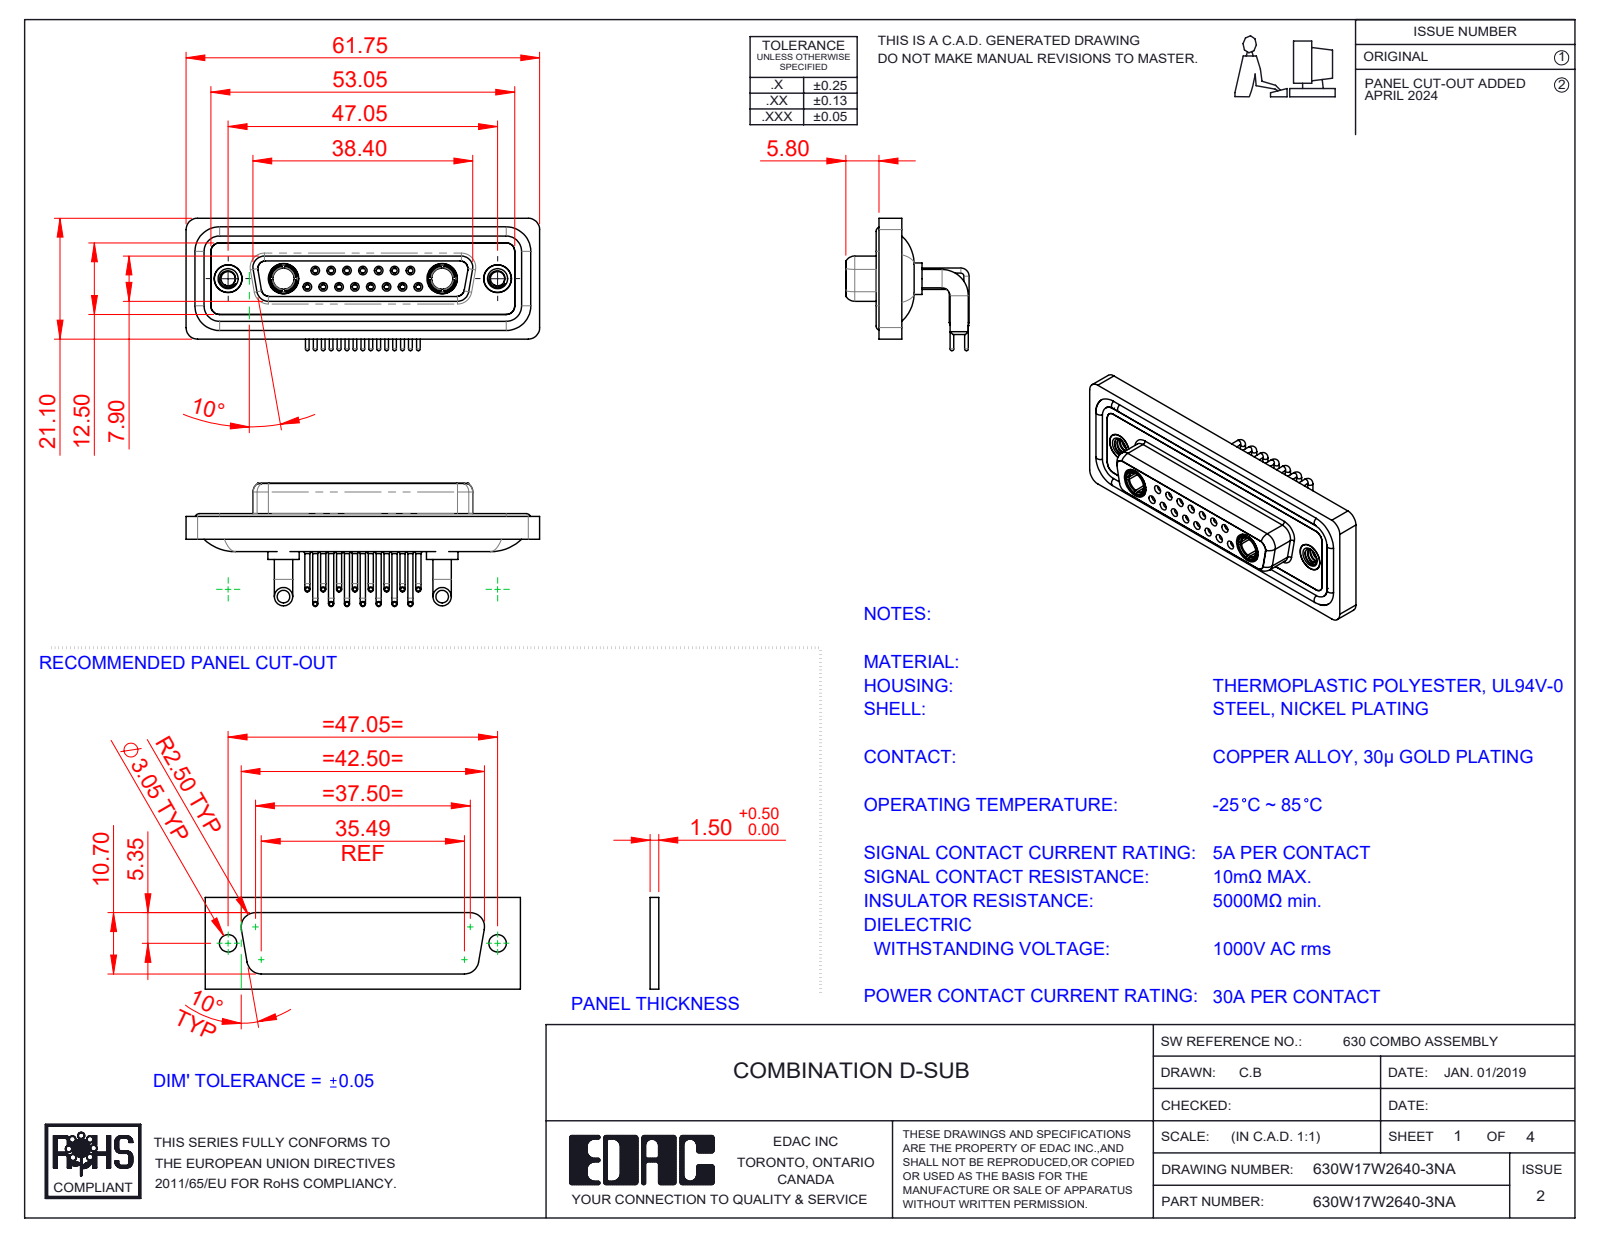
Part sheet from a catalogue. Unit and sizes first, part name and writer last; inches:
Units: inches
Overall size (bounding box): 2.431 × 0.91 × 0.848
Round holes (diameter × count): ⌀0.035 ×15, ⌀0.043 ×15, ⌀0.059 ×15, ⌀0.079 ×15, ⌀0.063 ×8, ⌀0.067 ×7, ⌀0.191 ×4, ⌀0.098 ×2, ⌀0.146 ×2, ⌀0.157 ×2, ⌀0.159 ×2, ⌀0.197 ×2
Round bosses / shafts (diameter × count): ⌀0.035 ×15, ⌀0.026 ×15, ⌀0.063 ×11, ⌀0.126 ×4, ⌀0.217 ×2, ⌀0.205 ×2, ⌀0.195 ×2, ⌀0.195 ×2
Partial cylindrical surfaces — rounded edges, fillets, slot ends (radius × count): R0.059 ×18, R0.079 ×18, R0.053 ×8, R0.063 ×8, R0.01 ×4, R0.02 ×4, R0.024 ×4, R0.026 ×4
Main face-to-face distances: 0.016, 0.071, 0.161, 0.043, 0.063, 0.122, 0.098, 0.059, 0.146, 0.055
Hole centre spacings: 0.124, 0.109, 0.218, 0.327, 0.198, 0.295, 0.436, 0.198
Volume: 0.521 in³ · Surface area: 22.58 in²
Bodies: 26 solids, 1331 faces (388 planar, 581 cylindrical, 362 other)
Part name (STEP PRODUCT): 630Combo Contact Row 2_50 Contacts; 630Combo Contact Row 1_50 Contacts; 630Combo Shell Rear_25 Contacts; 630Combo Threaded Rivet_A (+5 more)
STEP written by: SolidWorks 2023 (CONFIG_CONTROL_DESIGN)
